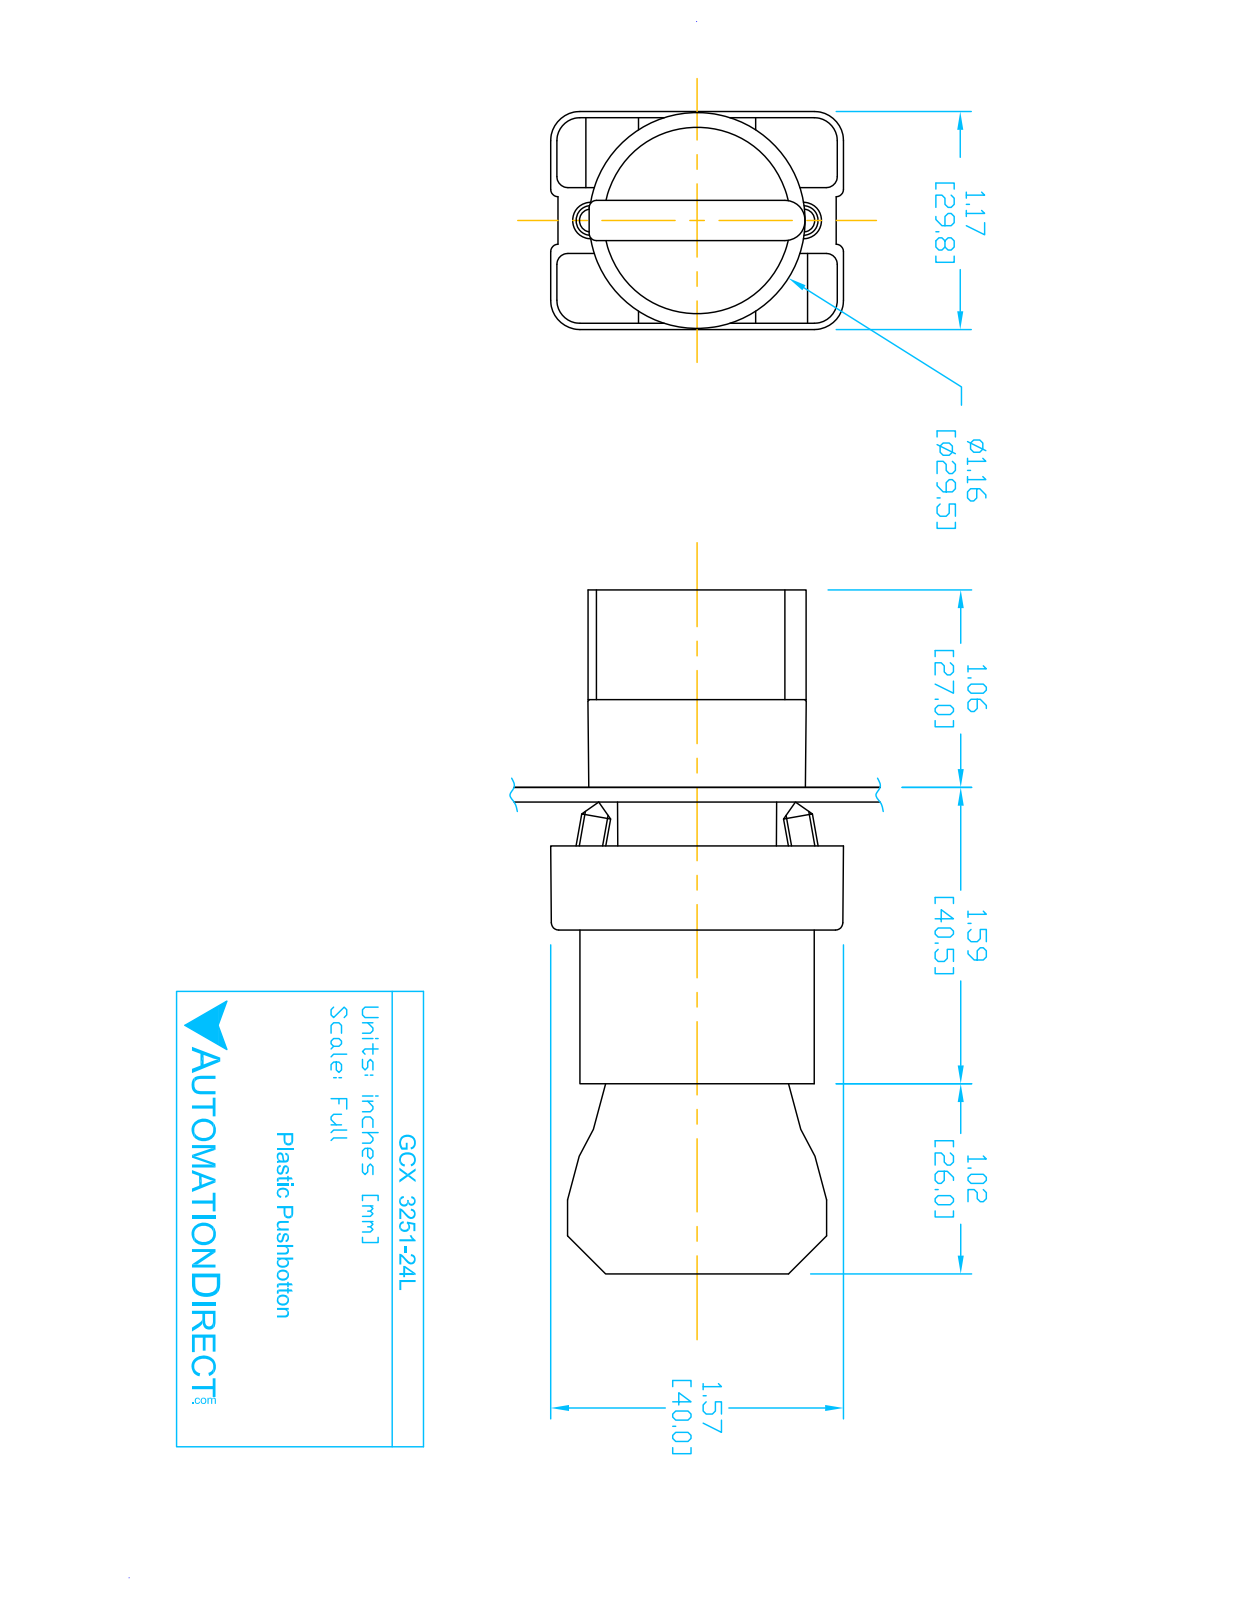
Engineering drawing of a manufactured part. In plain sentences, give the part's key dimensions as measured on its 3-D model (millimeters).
The part is named "ECX3029-2; GCX3251L OPERATOR; ECX1050; ecx1040 (+1 more)". Its 3-D file was written by "SolidWorks 2016 (AUTOMOTIVE_DESIGN)". It is 8 solids with 445 faces: 263 planar, 151 cylindrical and 31 other. Overall it measures 92.8 by 40.2 by 29.9 millimeters. Its volume is 45 870 cubic millimeters and its surface area 25 160 square millimeters. Round holes: 2 of diameter 2, 2 of diameter 3.1, 2 of diameter 3.3, 1 of diameter 2.2, 1 of diameter 5, 1 of diameter 11.9, 1 of diameter 22.3, 1 of diameter 22.6, 1 of diameter 26. Round bosses or shafts: 4 of diameter 4, 1 of diameter 29.8, 1 of diameter 25.5, 1 of diameter 24, 1 of diameter 21.7, 1 of diameter 19.8, 1 of diameter 12.8. Partial cylindrical surfaces (rounded edges, fillets, slot ends): 24 of radius 1.5, 12 of radius 1, 12 of radius 3.1, 12 of radius 4, 9 of radius 1, 2 of radius 3.3, 1 of radius 0.5, 1 of radius 1.6. The main face-to-face distances are 21, 51.3, 30.3, 14.7, 31.6, 29.7, 12, 11.9, 0.8, 0.8. The hole center spacings are 6, 13.8, 12, 12.4.
